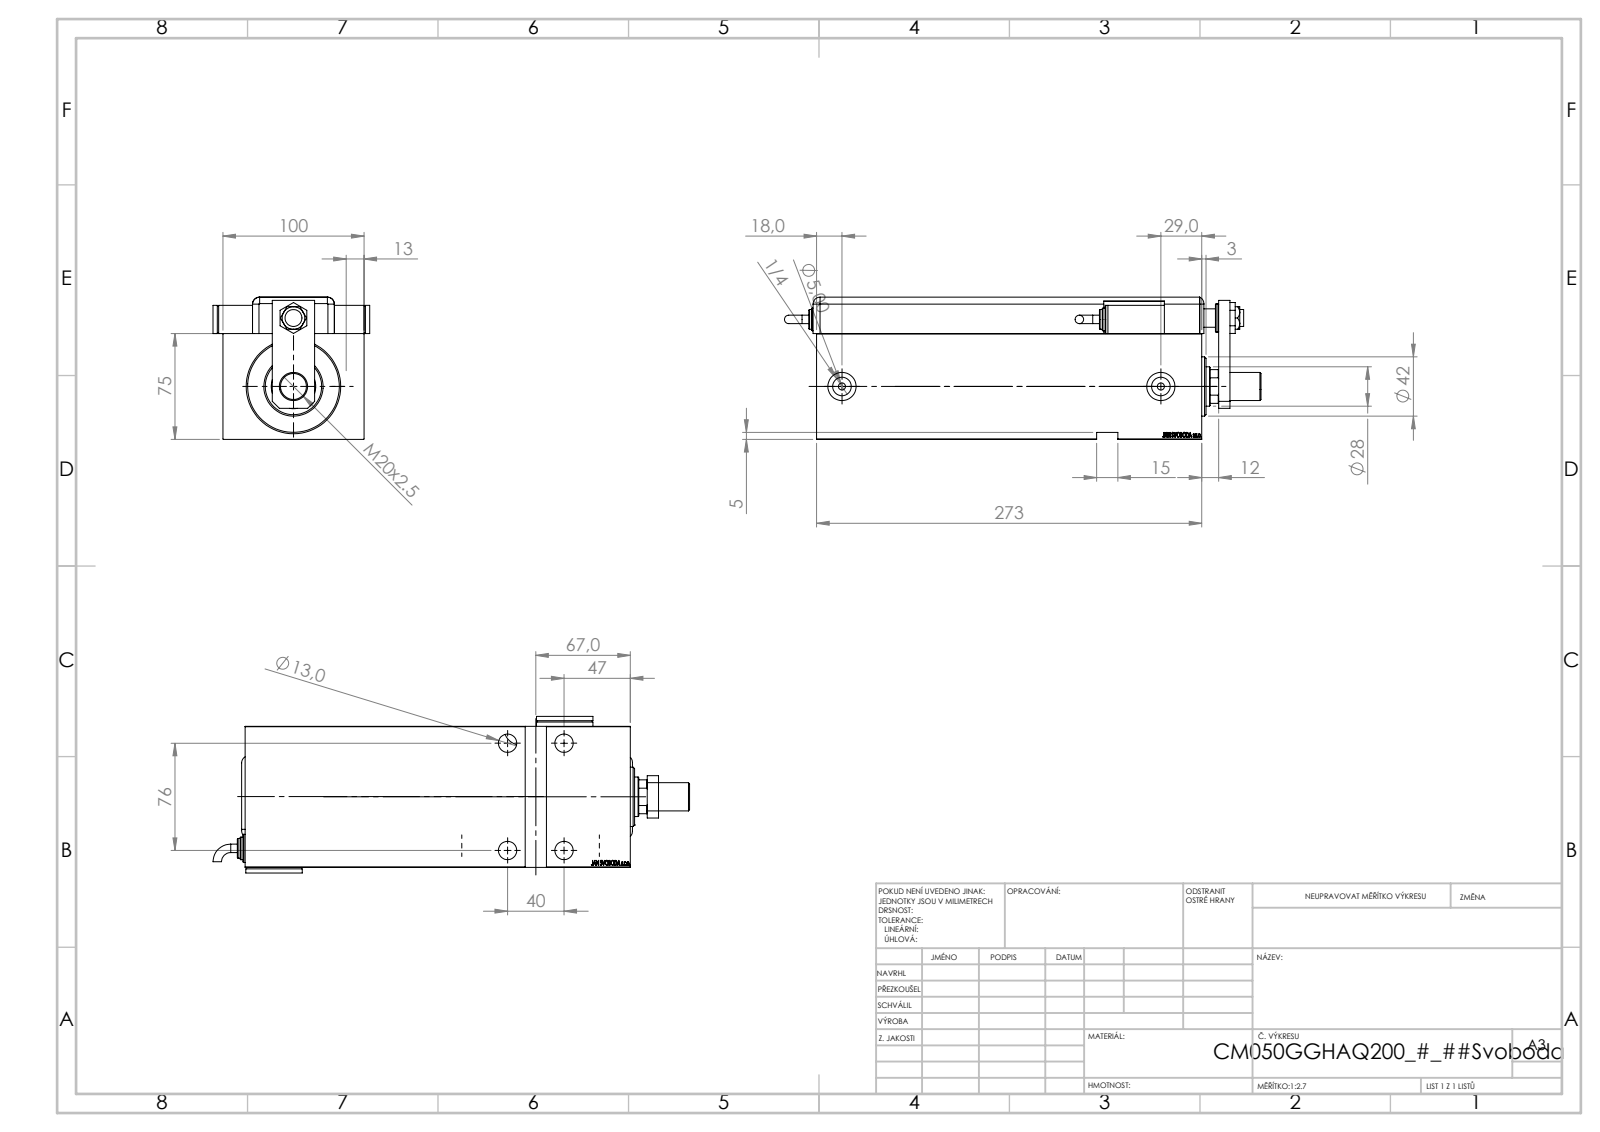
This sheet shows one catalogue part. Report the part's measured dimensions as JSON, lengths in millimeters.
{"part_name": "TYC; MAGNETIC SWITCH Q; Zatka_OIL_PORT; V450CM_G_Body (+8 more)", "step_written_by": "SolidWorks 2019 (CONFIG_CONTROL_DESIGN)", "units": "millimeters", "bodies": {"solids": 16, "faces": 1292, "planar": 650, "cylindrical": 115, "other": 527}, "overall_size": [337.76, 111, 100.8], "volume_mm3": 1939000, "surface_area_mm2": 308512, "round_holes": [[13, 5], [19, 4], [20, 3], [4, 2], [5, 2], [8, 2], [13.16, 2], [12, 1], [14, 1], [18.5, 1], [28, 1], [31.5, 1]], "round_bosses_or_shafts": [[20, 3], [18, 3], [16, 2], [14, 2], [6, 2], [42, 1]], "partial_cylinders_radius": [[5, 9], [10, 1], [13.5, 1]], "face_to_face_distances": [75, 3, 100, 100.8, 25.8, 22.8, 97.8, 21, 79, 76], "hole_center_spacings": [40, 47.2, 61.22, 76, 82.87, 85.88, 91.59, 20]}
